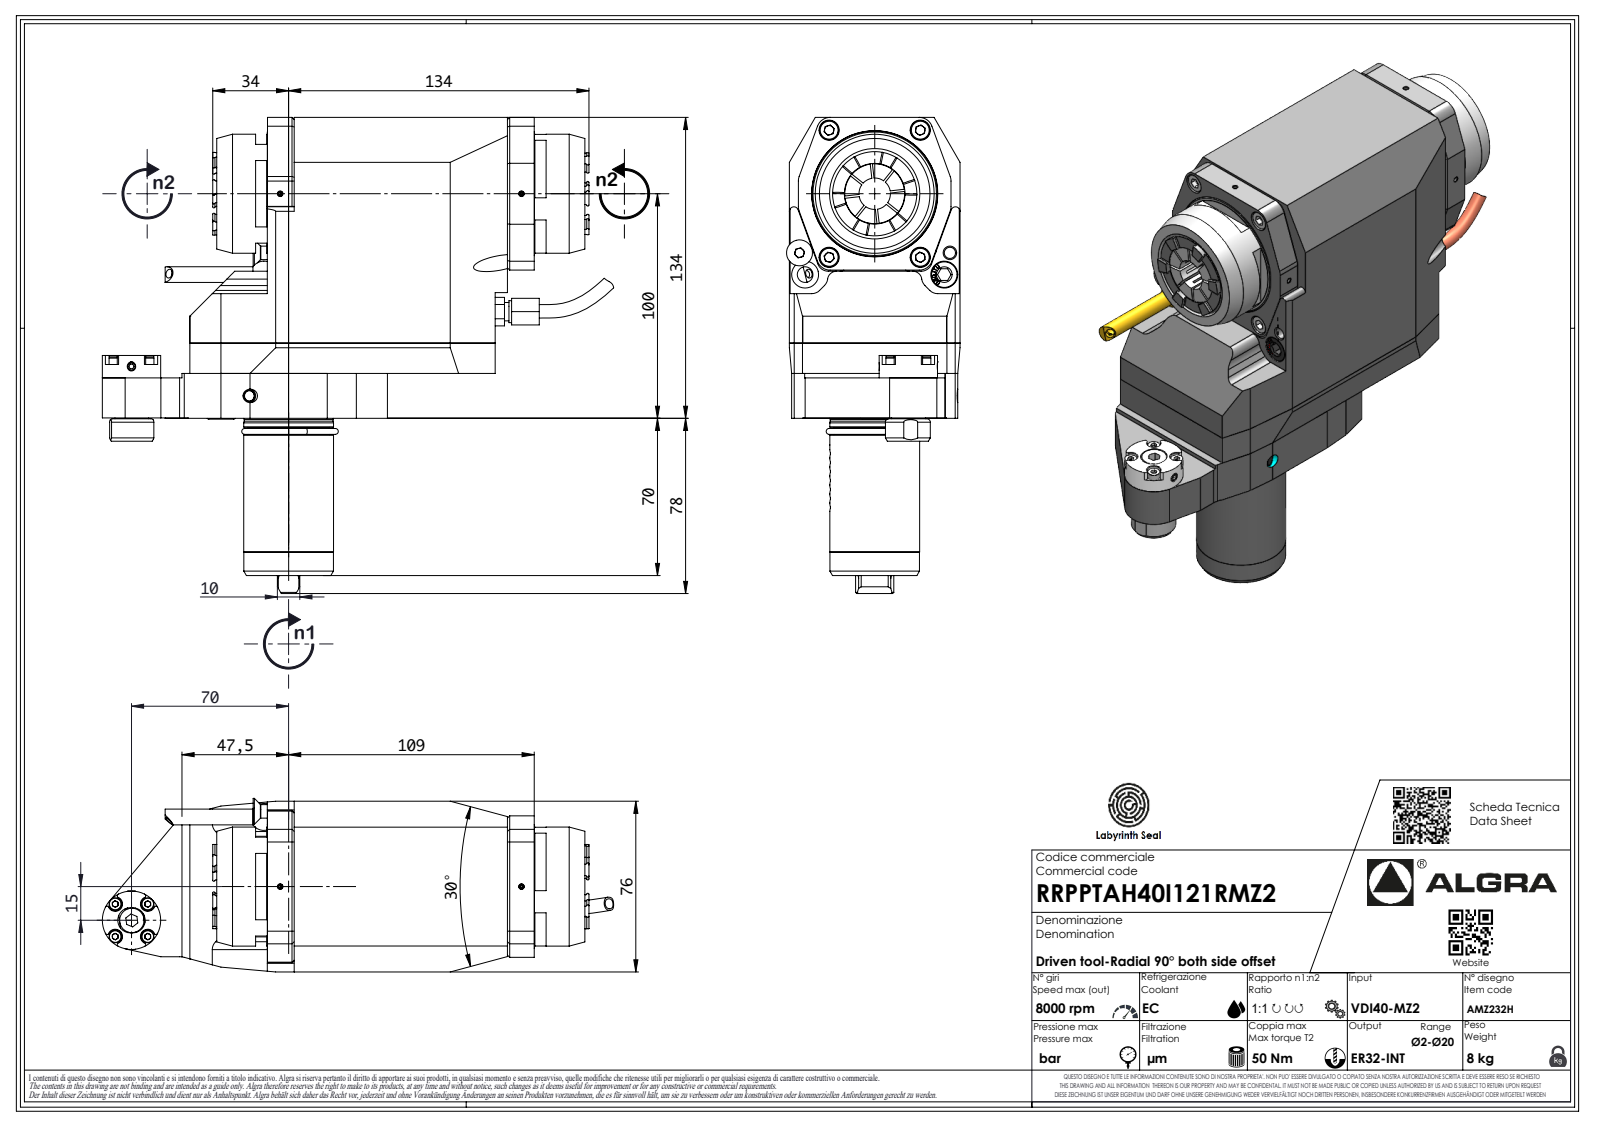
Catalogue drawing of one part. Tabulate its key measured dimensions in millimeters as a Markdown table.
| quantity | value |
| --- | --- |
| part name | RRPPTAH40I121RMZ2 |
| STEP written by | SolidWorks 2023 (AUTOMOTIVE_DESIGN) |
| units | millimeters |
| bodies | 1 solid, 621 faces (442 planar, 94 cylindrical, 85 other) |
| overall size | 227.81 × 212 × 76 |
| volume | 1 354 000 mm³ |
| surface area | 96 524 mm² |
| round holes (diameter × count) | 2.1 × 1, 4 × 1, 5 × 1, 6 × 1, 8.8 × 1 |
| round bosses / shafts (diameter × count) | 53 × 1, 40 × 1, 39.9 × 1, 39.6 × 1, 36 × 1, 26 × 1, 20 × 1, 15 × 1 |
| partial cylindrical surfaces (radius × count) | 6 × 10, 0.3 × 7, 0.33 × 7, 0.52 × 7, 3.7 × 7, 5 × 6, 2 × 3, 4 × 2 |
| main face-to-face distances | 76, 134, 20, 114, 88, 22.6, 141.4, 12, 136, 34.5 |
